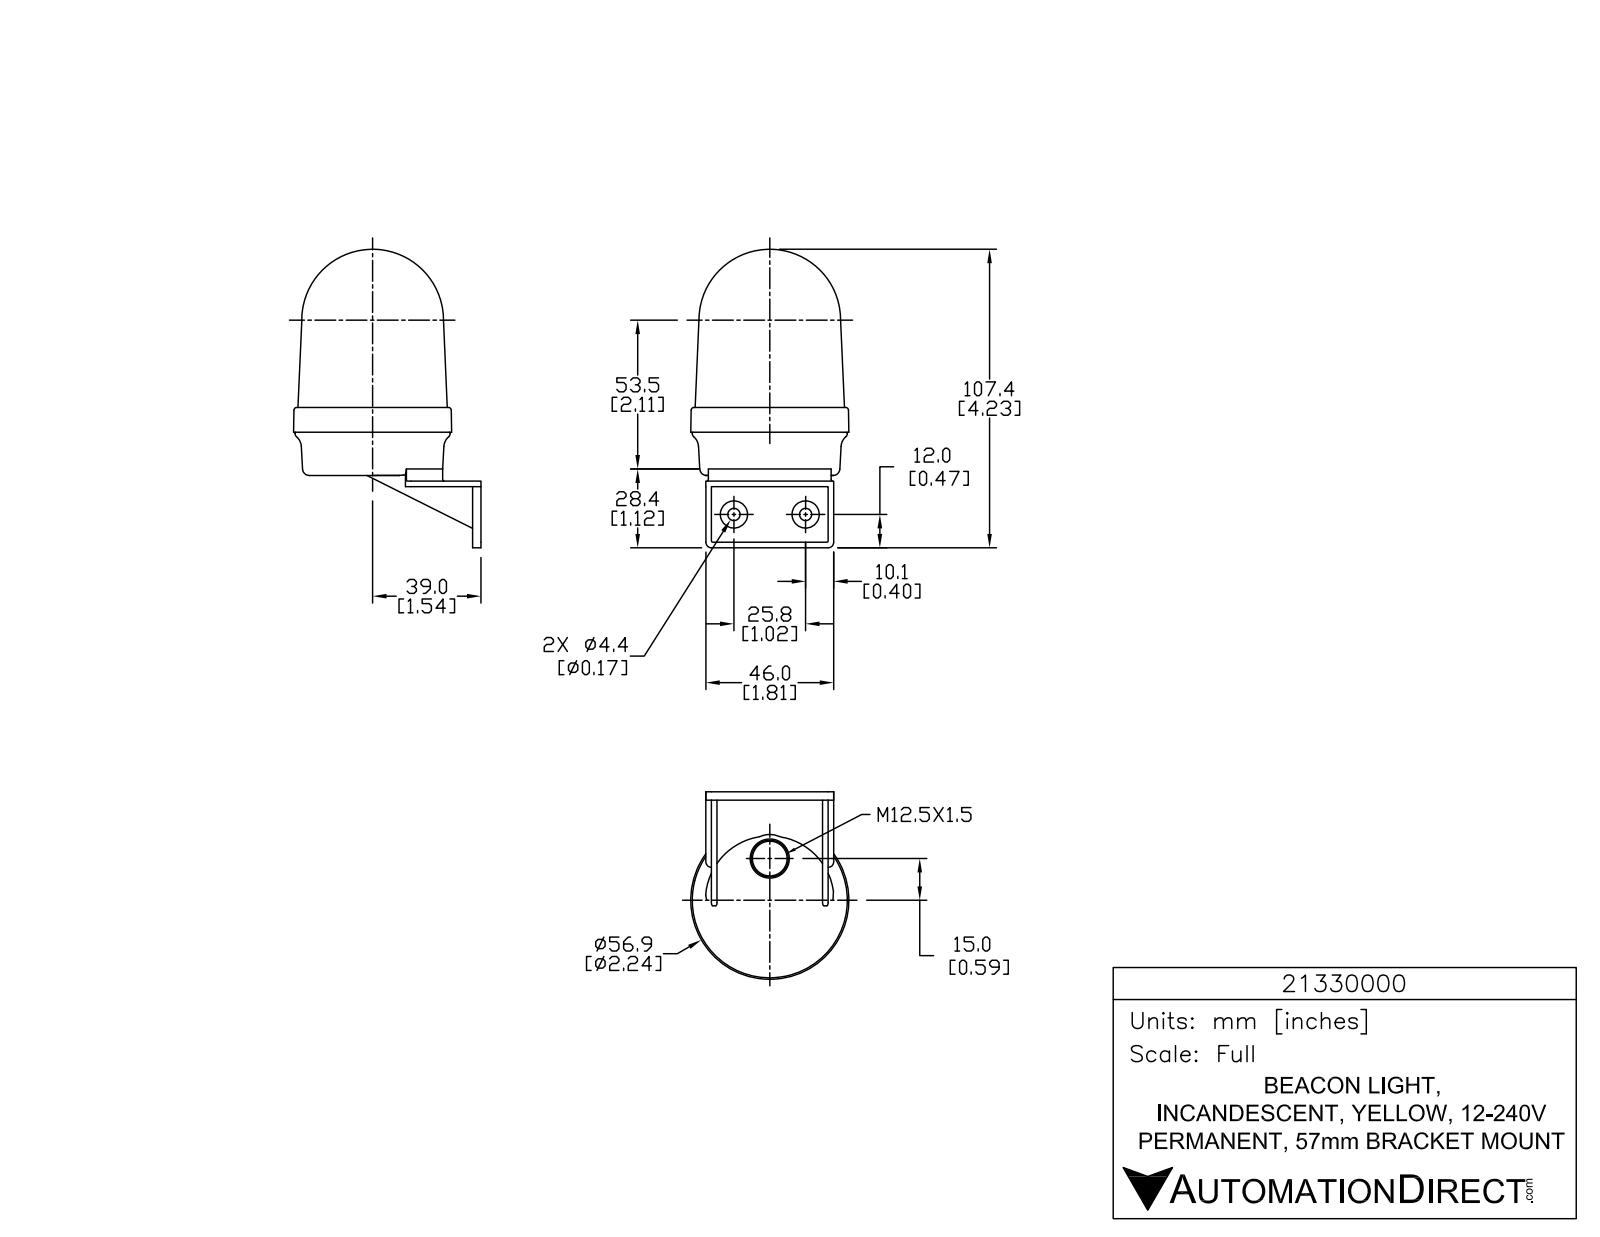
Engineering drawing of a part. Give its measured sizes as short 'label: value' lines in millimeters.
name: 21330000
written by: SolidWorks 2015 (AUTOMOTIVE_DESIGN)
unit: mm
bodies: 1 solid, 826 faces (550 planar, 178 cylindrical, 98 other)
size: 107.4 × 72.1 × 60.8
volume: 162 800 mm³; area: 21 270 mm²
holes: 3× ⌀1, 2× ⌀4.4
bosses: 3× ⌀5.7, 3× ⌀1.4, 2× ⌀9.8, 1× ⌀55.8
rounds: 6× R0.2, 6× R0.2, 6× R0.2, 6× R0.5, 6× R3.3, 4× R2, 3× R0.1, 3× R0.1
face distances: 2, 4, 40, 42, 1, 3, 38, 22, 24, 19.6
hole spacings: 25.8
